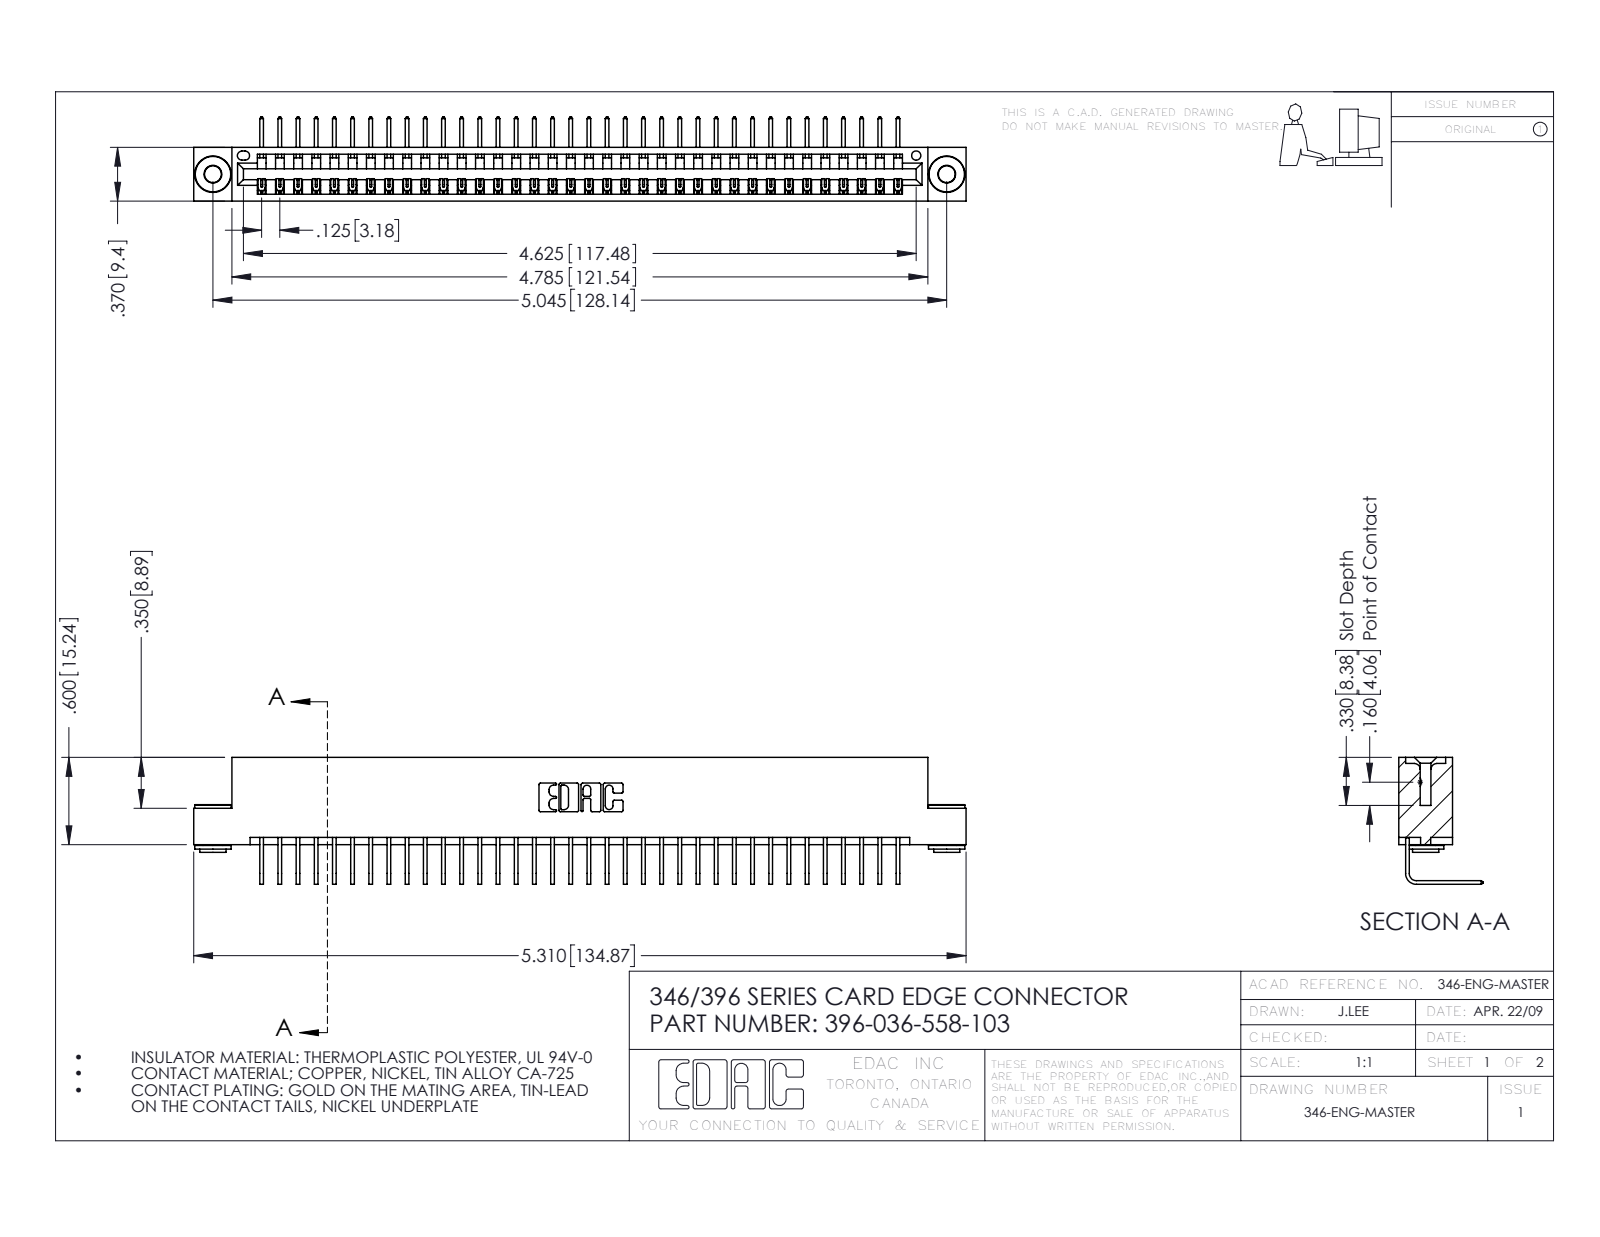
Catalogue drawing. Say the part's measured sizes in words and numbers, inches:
The part is named "346 Part_Flush Mounting Lugs - 0.156 Dia-TH; 345-292-001_558 Tail - 2; 396-036-558-103; 345-250-002_345-250-002-102". Its 3-D file was written by "SolidWorks 2016 (CONFIG_CONTROL_DESIGN)". It is 39 solids with 2320 faces: 1598 planar, 714 cylindrical and 8 other. Overall it measures 5.31 by 0.873 by 0.58 inches. Its volume is 0.794 cubic inches and its surface area 26.55 square inches. Round holes: 2 of diameter 0.116, 2 of diameter 0.156, 1 of diameter 0.064. Round bosses or shafts: 2 of diameter 0.25, 2 of diameter 0.18, 2 of diameter 0.136. Partial cylindrical surfaces (rounded edges, fillets, slot ends): 72 of radius 0.006, 22 of radius 0.01, 6 of radius 0.007, 6 of radius 0.031, 3 of radius 0.026, 2 of radius 0.031, 2 of radius 0.04, 1 of radius 0.014. The main face-to-face distances are 0.322, 0.048, 0.37, 0.25, 0.025, 0.298, 0.072, 0.148, 0.222, 0.1. The hole center spacings are 0.246, 4.836, 5.045.
